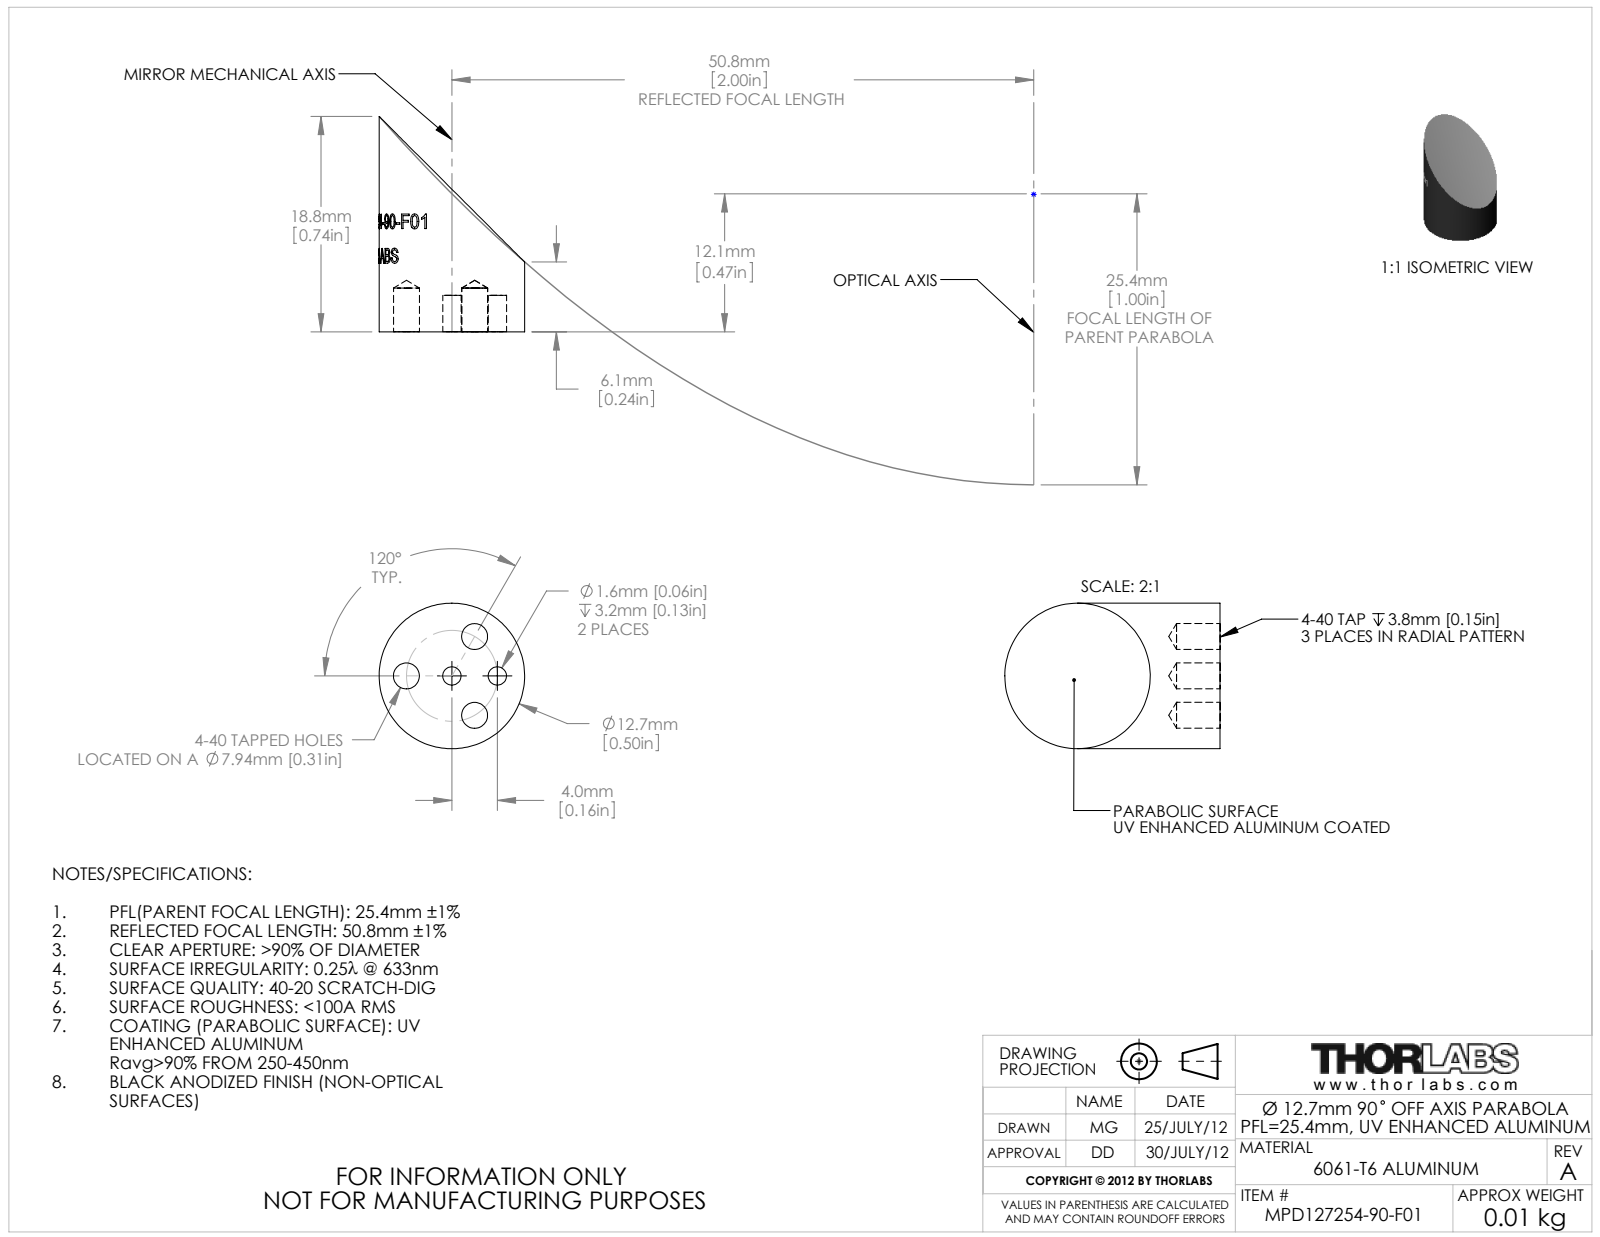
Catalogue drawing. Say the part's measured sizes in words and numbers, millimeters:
The part is named "24687-E0W". Its 3-D file was written by "SolidWorks 2012 (CONFIG_CONTROL_DESIGN)". It is 1 solid with 58 faces: 3 planar, 47 cylindrical and 8 other. Overall it measures 18.8 by 12.7 by 12.7 millimeters. Its volume is 1 490 cubic millimeters and its surface area 918 square millimeters. Round holes: 3 of diameter 2.26, 2 of diameter 1.6. Round bosses or shafts: 1 of diameter 12.7. The main face-to-face distances are 3.17. The hole center spacings are 3.97, 6.87, 6.88, 7.94.
